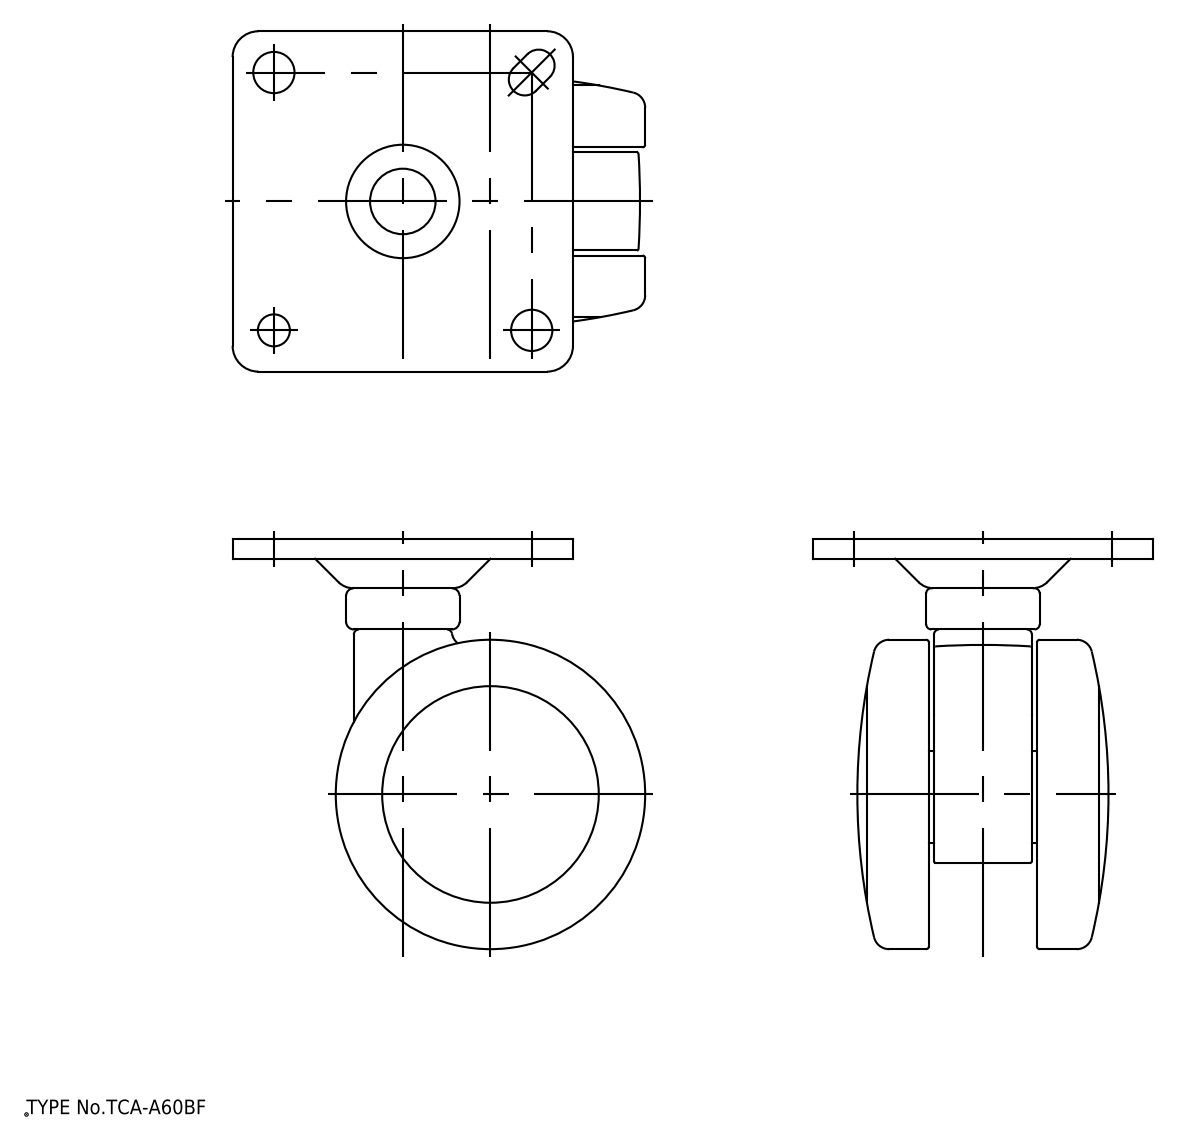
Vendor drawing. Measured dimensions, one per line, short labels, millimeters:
name: A60; TY75 ___t; A60 _{
written by: spGate 18.9.1 (****-****-****-****) (AUTOMOTIVE_DESIGN)
unit: mm
bodies: 4 solids, 203 faces (33 planar, 62 cylindrical, 108 other)
size: 80 × 79.5 × 66
volume: 112 314 mm³; area: 46 374 mm²
holes: 2× ⌀8, 1× ⌀6.2, 1× ⌀9.1, 1× ⌀12, 1× ⌀21.5, 1× ⌀25, 1× ⌀43.5, 1× ⌀44
bosses: 1× ⌀60, 1× ⌀42, 1× ⌀22, 1× ⌀19, 1× ⌀11, 1× ⌀9
rounds: 4× R0.3, 4× R5, 2× R3.1, 1× R9.5, 1× R13.25
face distances: 31, 6, 1, 11, 12, 3.8, 5, 32, 20, 37
hole spacings: 35.36, 50, 70.71
